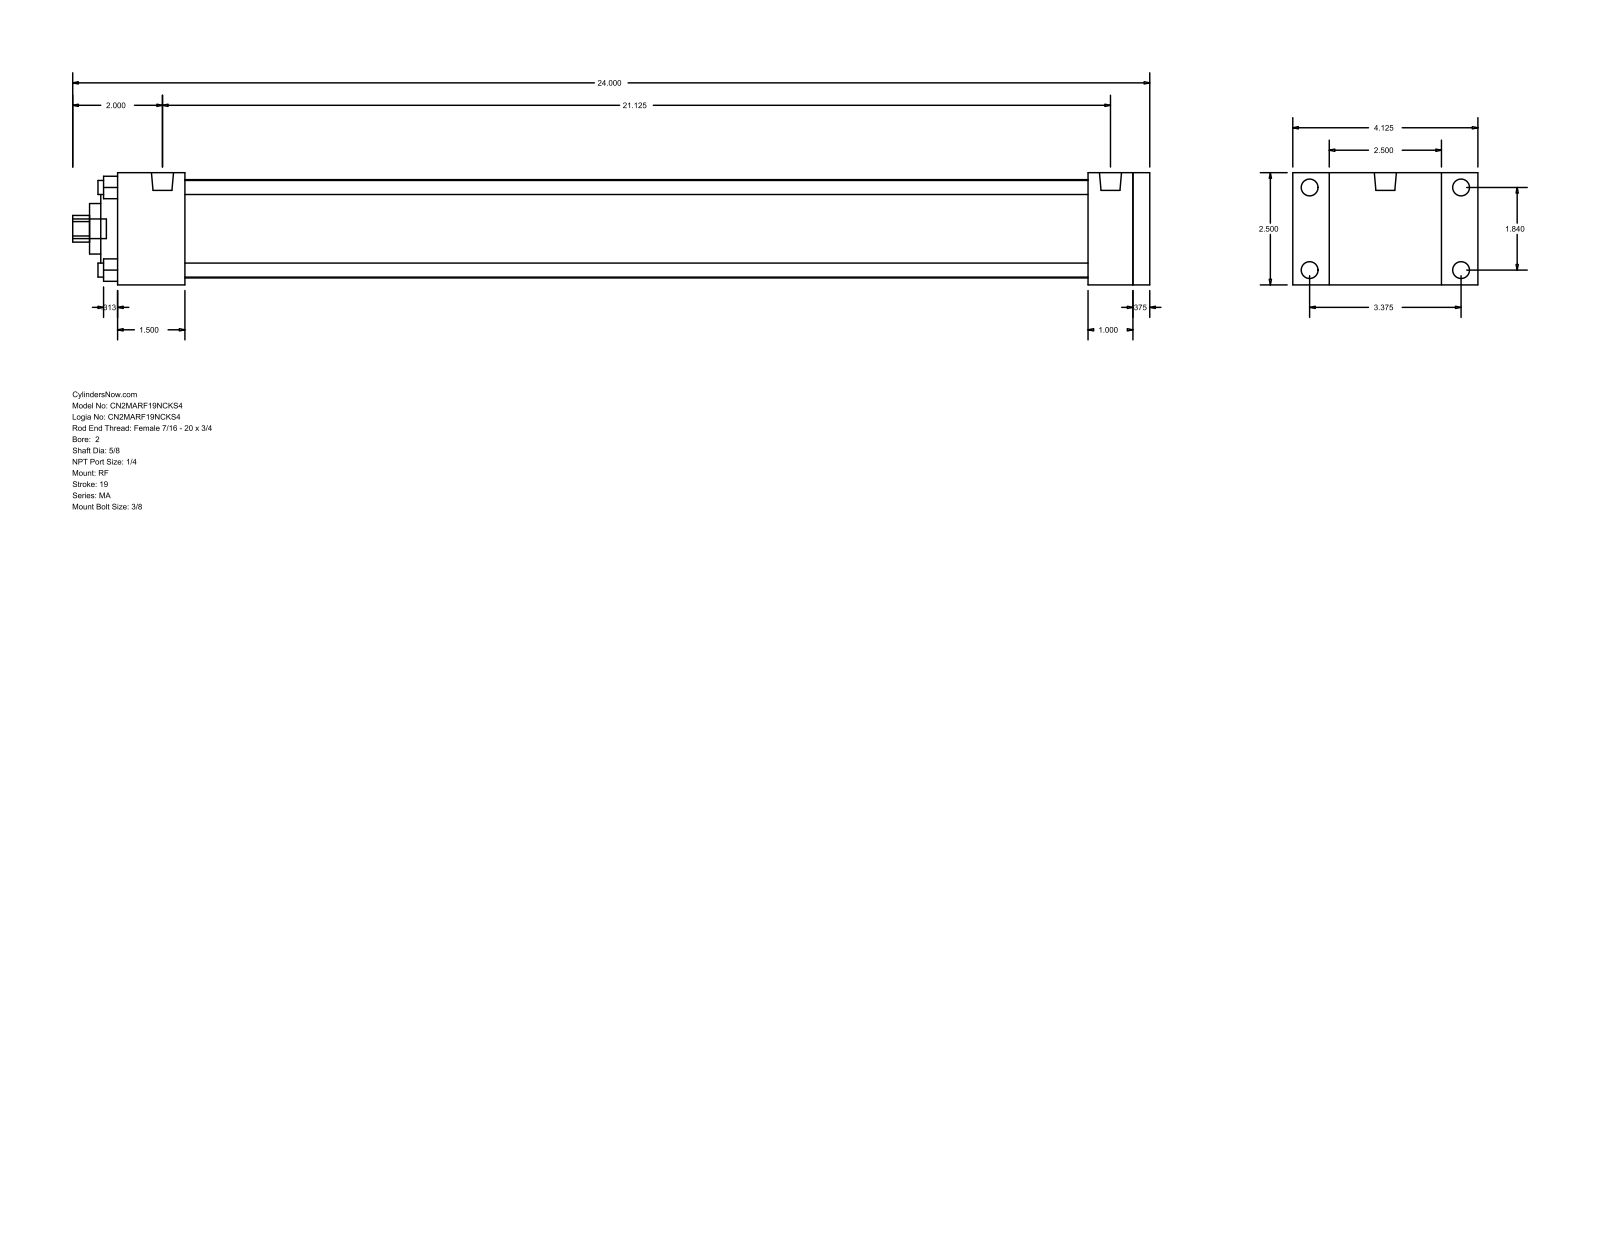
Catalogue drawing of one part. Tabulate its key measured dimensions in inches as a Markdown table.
| quantity | value |
| --- | --- |
| part name | MA_RF__0200_0.625 |
| STEP written by | GSSL Pune (CONFIG_CONTROL_DESIGN) |
| units | inches |
| bodies | 0 solids, 94 faces (65 planar, 29 cylindrical, 0 other) |
| overall size | 24 × 4.125 × 2.5 |
| round holes (diameter × count) | 0.313 × 4, 0.625 × 1, 1.125 × 1, 2 × 1, 2.19 × 1 |
| round bosses / shafts (diameter × count) | 0.375 × 4, 0.313 × 4, 0.492 × 2, 0.437 × 1 |
| partial cylindrical surfaces (radius × count) | 0.297 × 1 |
| main face-to-face distances | 2.5, 0.375, 23, 1.5, 22.625, 21.125, 21.5, 21.625, 20.125, 1 |
| hole center spacings | 1.301, 1.84, 2.602 |
